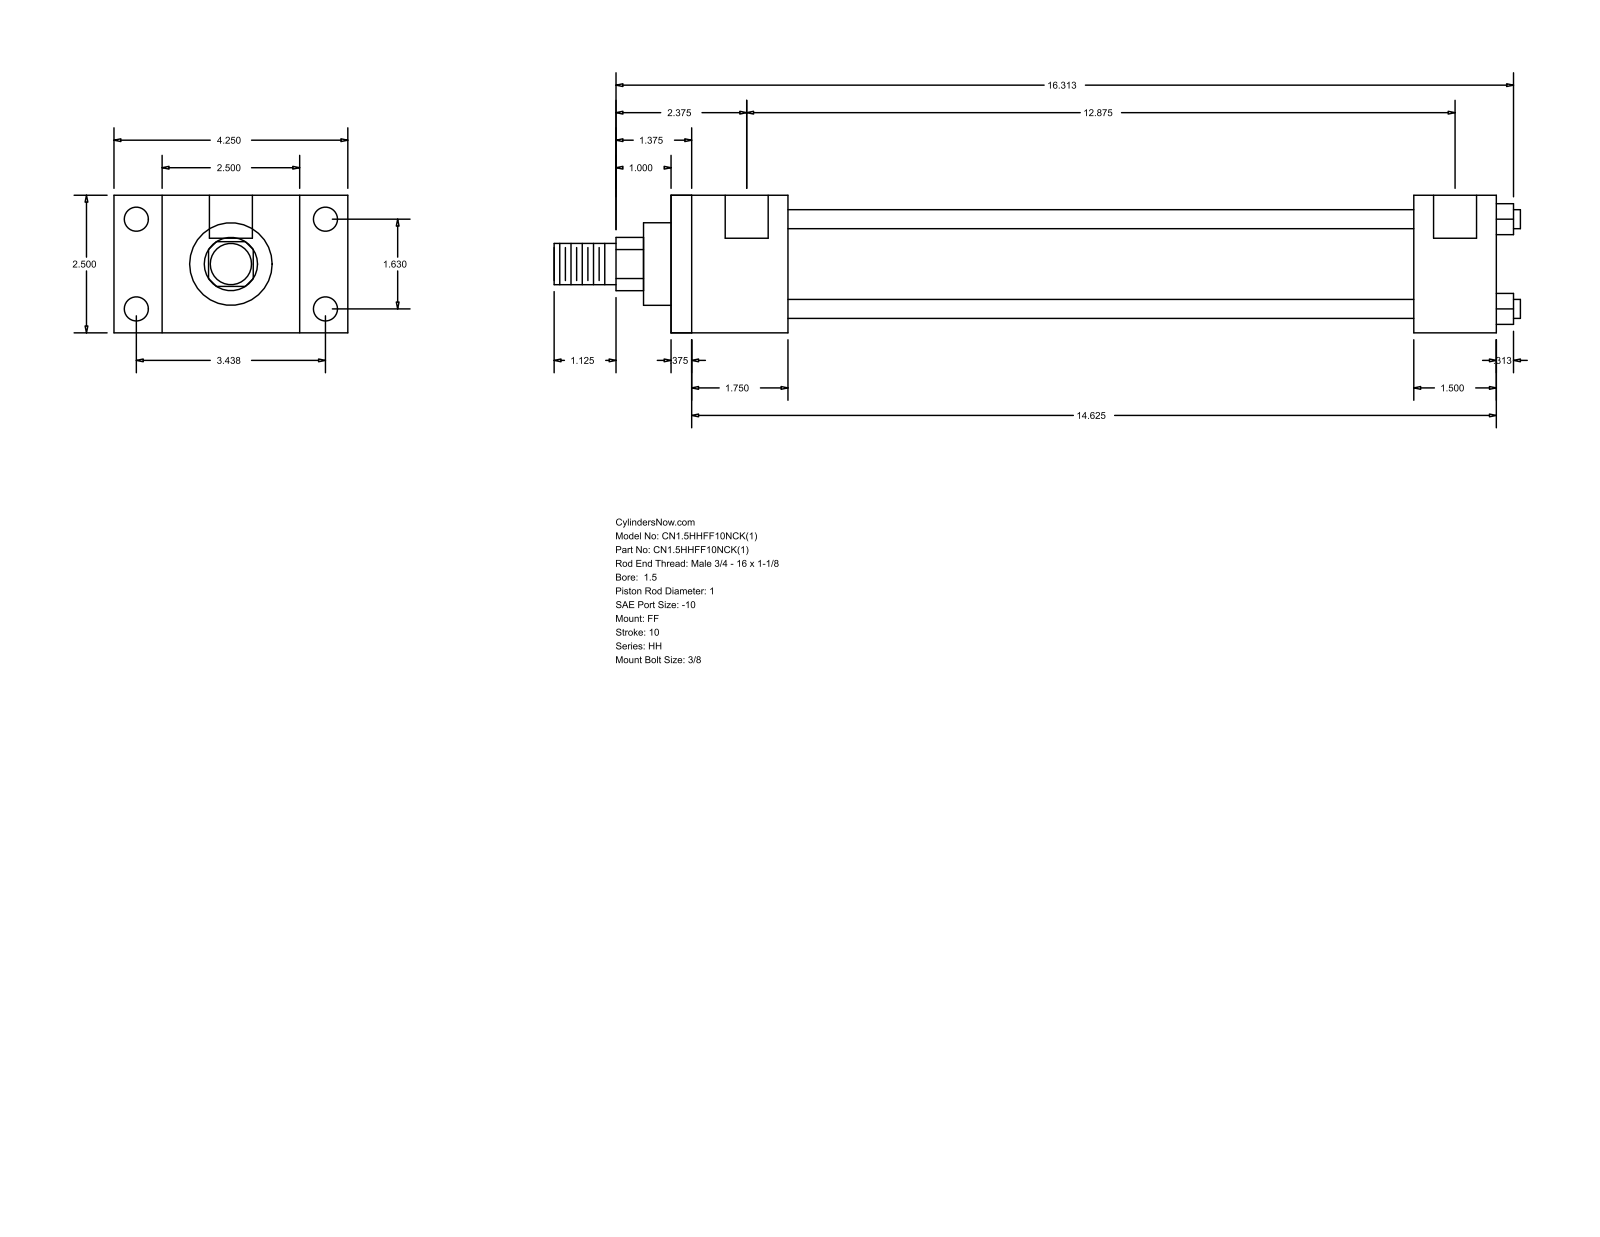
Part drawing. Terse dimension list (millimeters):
name: HH_FF__0150_1
written by: GSSL Pune (CONFIG_CONTROL_DESIGN)
unit: mm
bodies: 0 solids, 92 faces (64 planar, 28 cylindrical, 0 other)
size: 446.09 × 107.95 × 63.5
holes: 4× ⌀5.56, 4× ⌀11.13, 2× ⌀19.84
bosses: 4× ⌀8.76, 1× ⌀44.45, 1× ⌀38.1, 1× ⌀25.4, 1× ⌀19.05
rounds: 1× R12.29
face distances: 63.5, 381, 9.52, 371.48, 38.1, 53.98, 44.46, 327.02, 342.9, 333.38
hole spacings: 1.59, 41.4, 87.32, 96.64, 328.61, 330.2, 327.02
